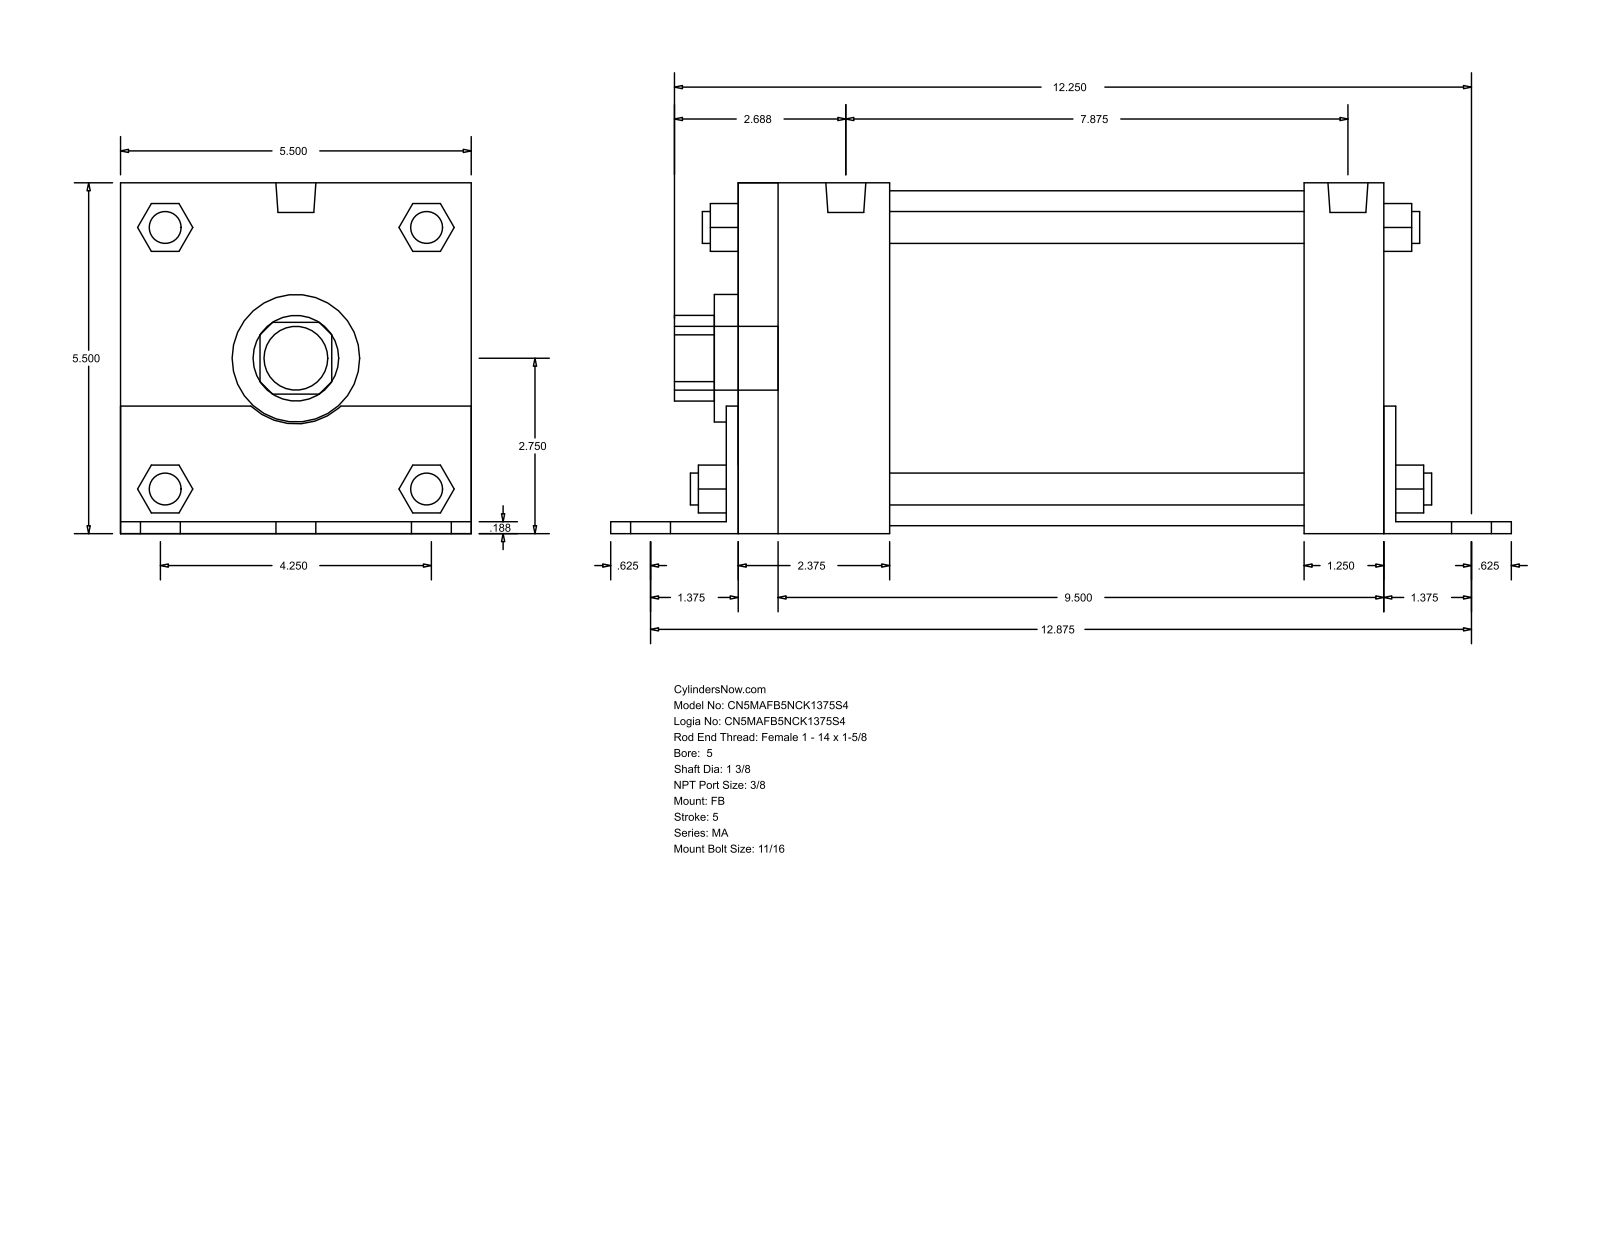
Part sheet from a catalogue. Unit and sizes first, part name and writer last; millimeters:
Units: millimetres
Overall size (bounding box): 358.77 × 139.75 × 139.7
Round holes (diameter × count): ⌀34.92 ×1, ⌀50.8 ×1, ⌀133.35 ×1
Round bosses / shafts (diameter × count): ⌀17.46 ×6, ⌀12.7 ×4, ⌀11.11 ×4, ⌀15.93 ×2, ⌀25.4 ×1
Partial cylindrical surfaces — rounded edges, fillets, slot ends (radius × count): R17.06 ×1, R26.16 ×1
Main face-to-face distances: 139.7, 4.76, 139.75, 4.71, 134.99, 257.17, 4.77, 261.94, 261.93, 266.7
Bodies: 0 solids, 140 faces (105 planar, 35 cylindrical, 0 other)
Part name (STEP PRODUCT): MA_FB__0500_1.375
STEP written by: GSSL Pune (CONFIG_CONTROL_DESIGN)
